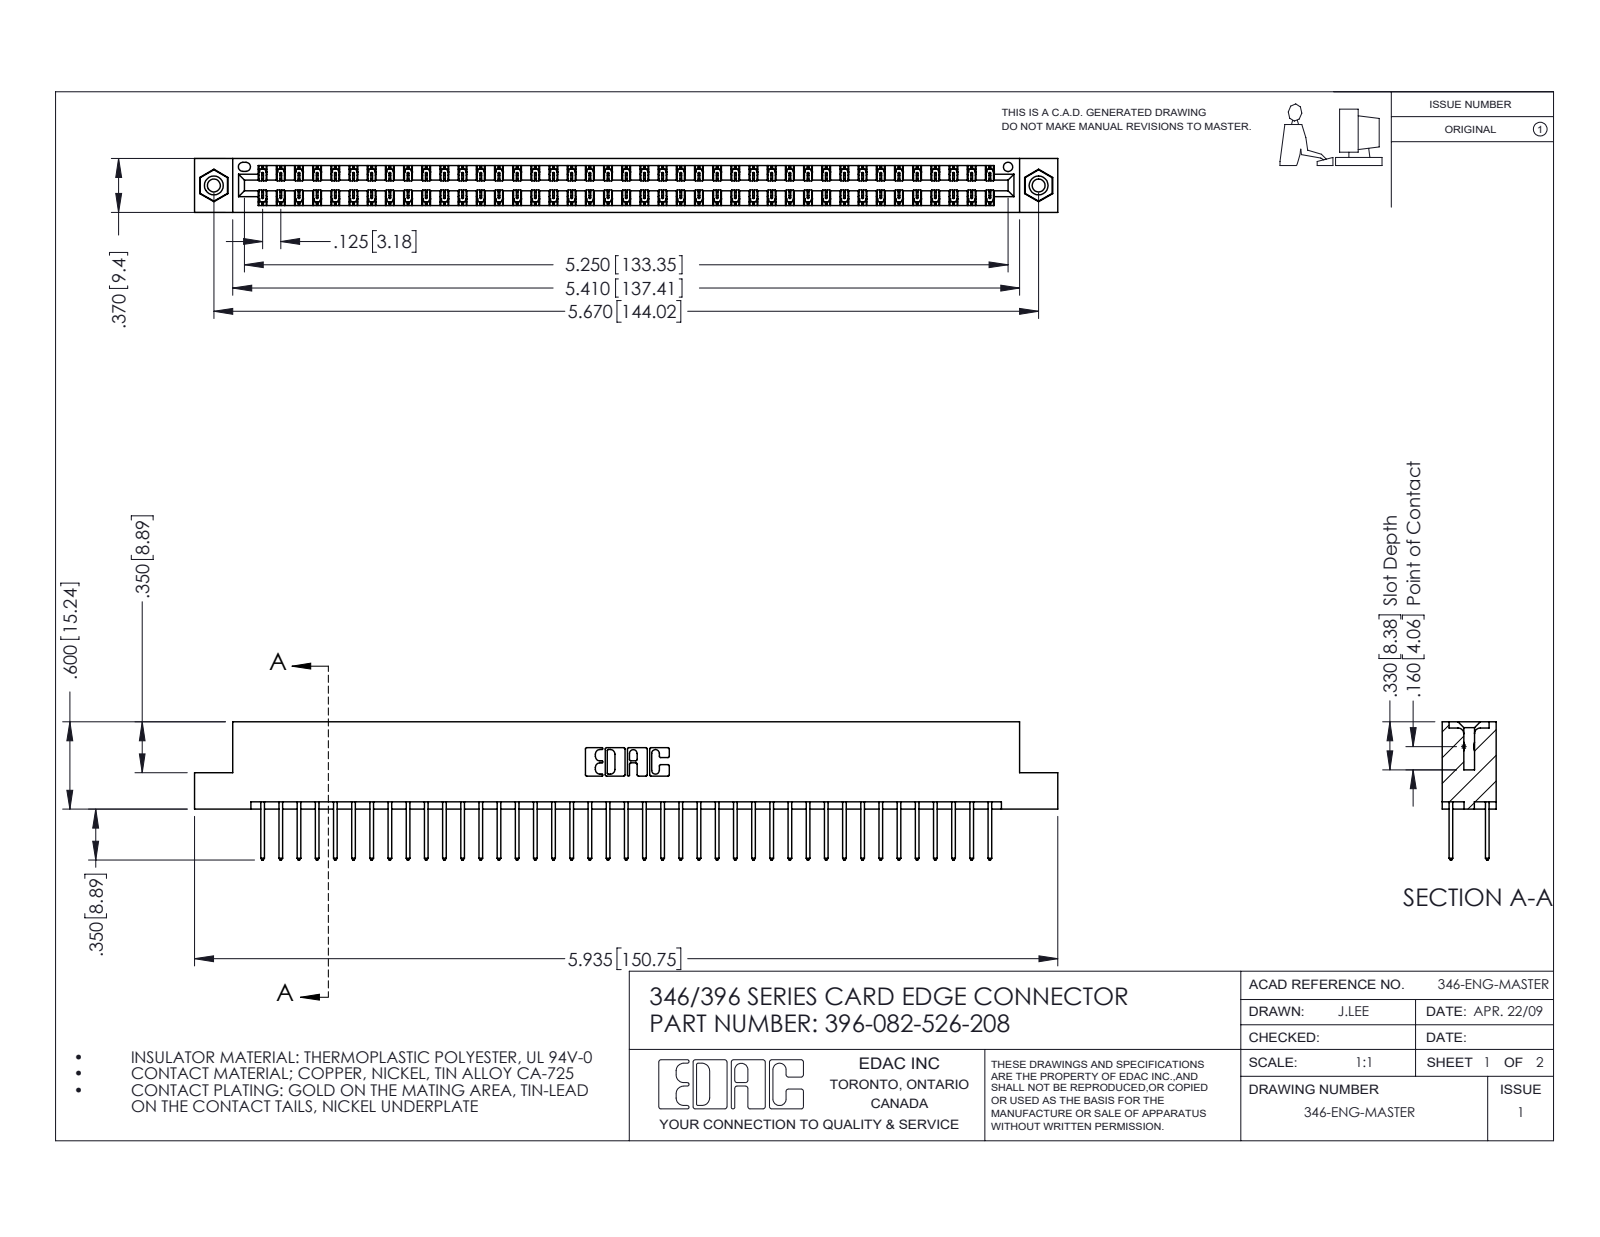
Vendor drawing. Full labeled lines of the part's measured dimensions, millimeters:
Part name (STEP PRODUCT): 345-250-001_345-250-003-102; 346 Part_Flush Mounting Lugs - 0.156 Dia-TI; 345-292-001_345-293-126; 396-082-526-208
STEP written by: SolidWorks 2016 (CONFIG_CONTROL_DESIGN)
Units: millimetres
Bodies: 85 solids, 4446 faces (2978 planar, 1452 cylindrical, 16 other)
Overall size (bounding box): 150.7 × 24.1 × 9.4
Volume: 14 800 mm³ · Surface area: 20 970 mm²
Round holes (diameter × count): ⌀2.3 ×2, ⌀3.2 ×2, ⌀4 ×2, ⌀1.6 ×1
Round bosses / shafts (diameter × count): ⌀3.9 ×2
Partial cylindrical surfaces — rounded edges, fillets, slot ends (radius × count): R0.2 ×123, R0.3 ×82, R0.3 ×22, R0.2 ×6, R0.8 ×6, R0.7 ×3, R0.4 ×2, R0.6 ×2
Main face-to-face distances: 1.2, 8.2, 6.4, 9.4, 1.8, 7.6, 0.6, 7, 3.8, 5.6
Hole centre spacings: 6.2, 138.7, 144
